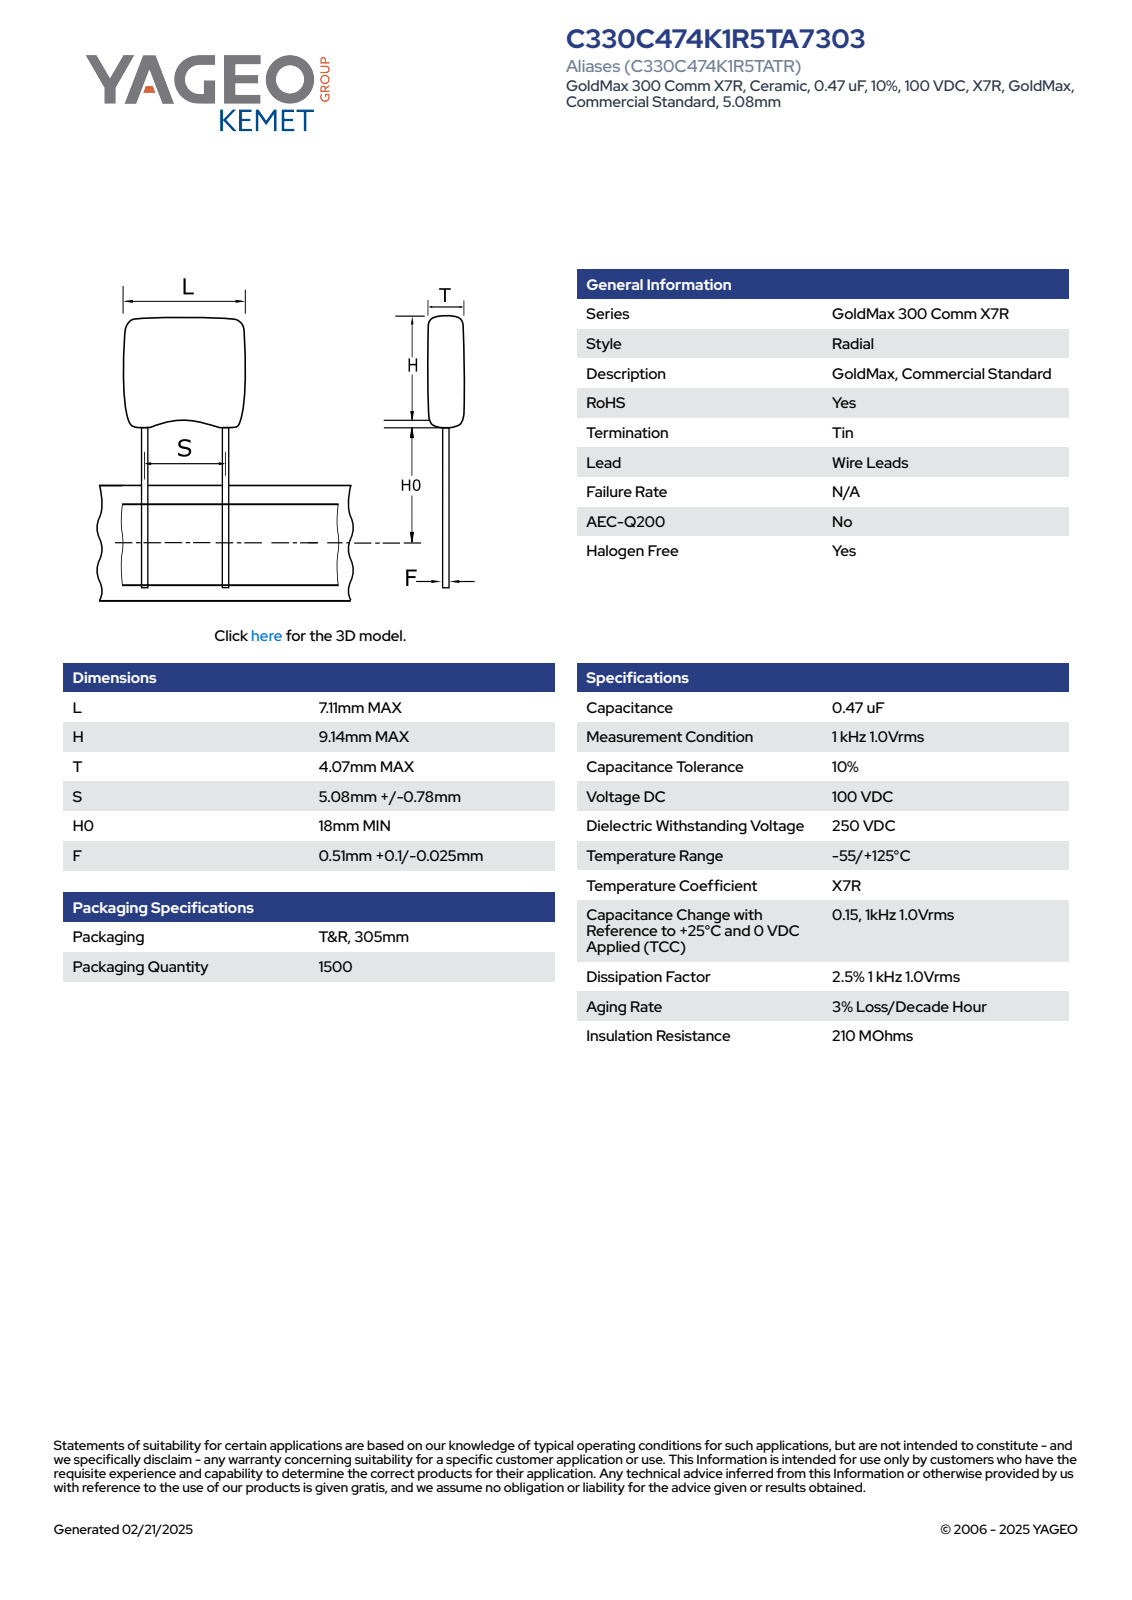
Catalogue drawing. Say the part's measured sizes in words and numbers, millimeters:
The part is named "CCR_KRCST_C330_L7.11H9.14T4.07S5.08H018F0.61". Its 3-D file was written by "SolidWorks 2014 (AUTOMOTIVE_DESIGN)". It is 4 solids with 98 faces: 70 planar, 18 cylindrical and 10 other. Overall it measures 28.18 by 7.11 by 4.08 millimeters. Its volume is 283 cubic millimeters and its surface area 328 square millimeters. Round bosses or shafts: 2 of diameter 0.61. Partial cylindrical surfaces (rounded edges, fillets, slot ends): 12 of radius 0.75. The main face-to-face distances are 4.07, 7.11, 10.18, 4.08, 18, 28.18, 23.24, 5.24, 4.94, 22.52.
